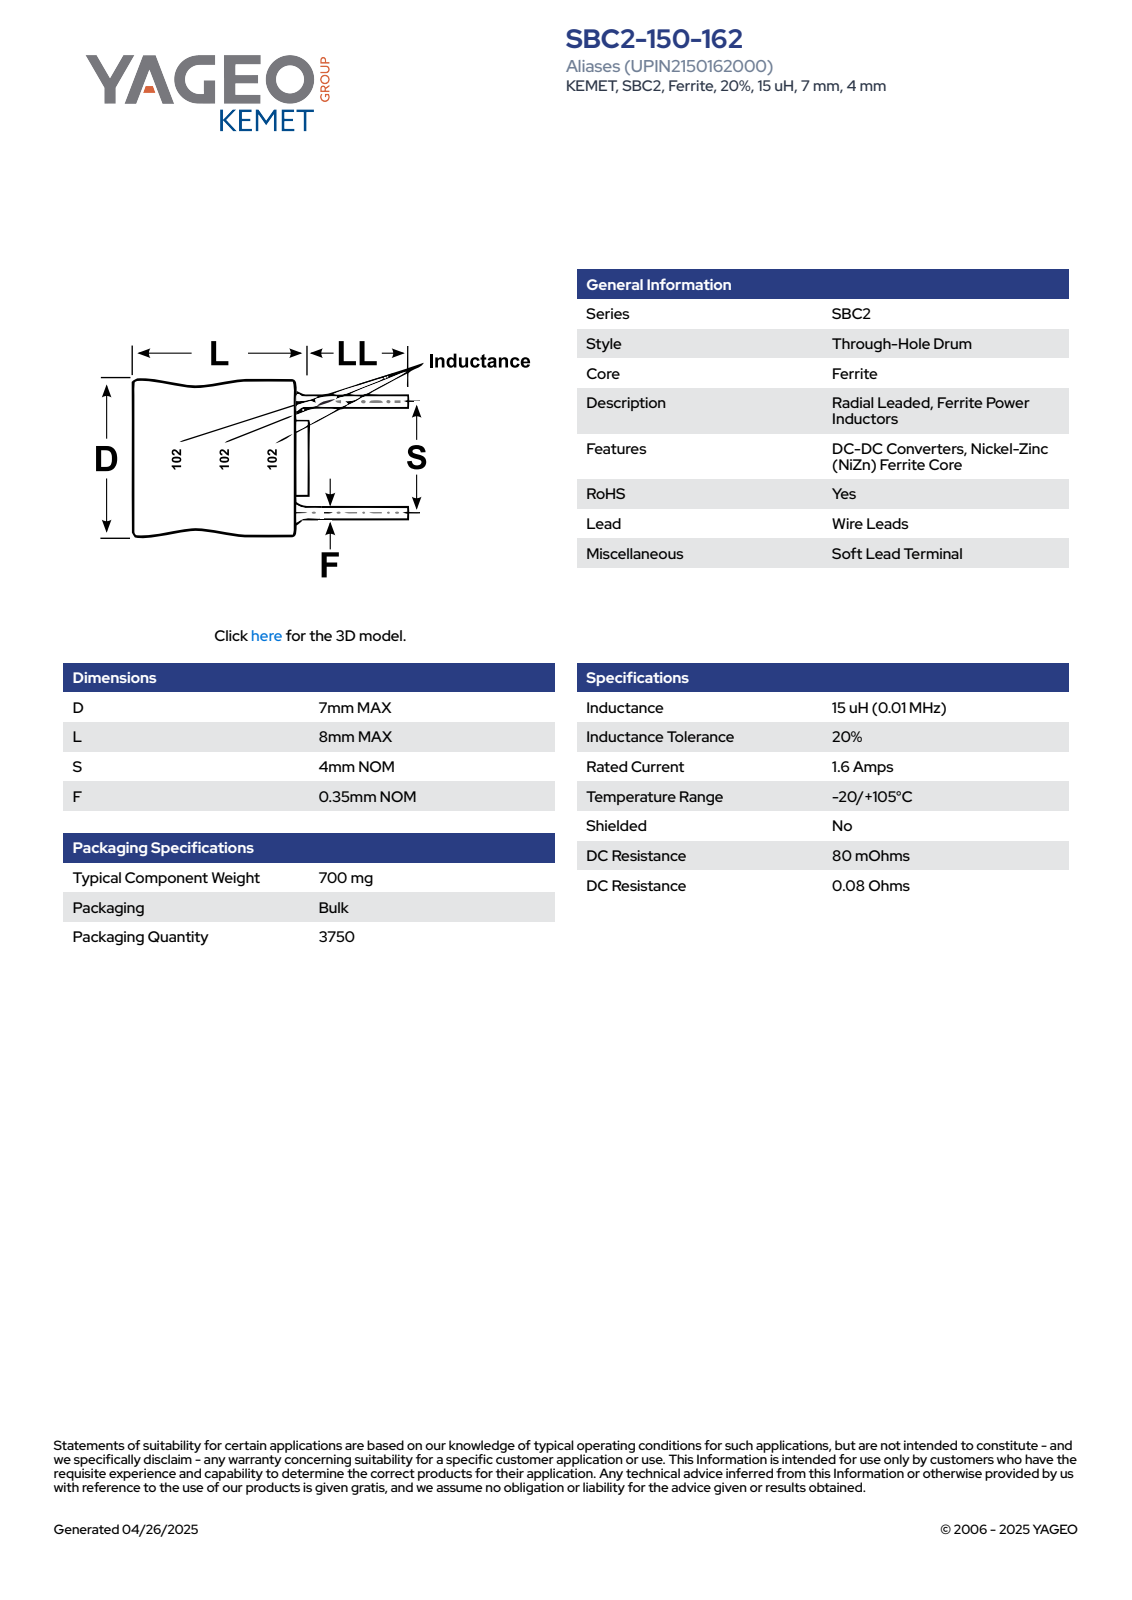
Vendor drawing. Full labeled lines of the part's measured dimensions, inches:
Part name (STEP PRODUCT): IL_SBCP_D7L8S4LL4.5F0.35
STEP written by: SolidWorks 2014 (AUTOMOTIVE_DESIGN)
Units: inches
Bodies: 4 solids, 84 faces (66 planar, 10 cylindrical, 8 other)
Overall size (bounding box): 0.493 × 0.276 × 0.276
Volume: 0.016 in³ · Surface area: 0.394 in²
Round bosses / shafts (diameter × count): ⌀0.014 ×2, ⌀0.276 ×1, ⌀0.251 ×1
Main face-to-face distances: 0.306, 0.306, 0.315, 0.315, 0.177, 0.187, 0.492, 0.493, 0.105, 0.015
